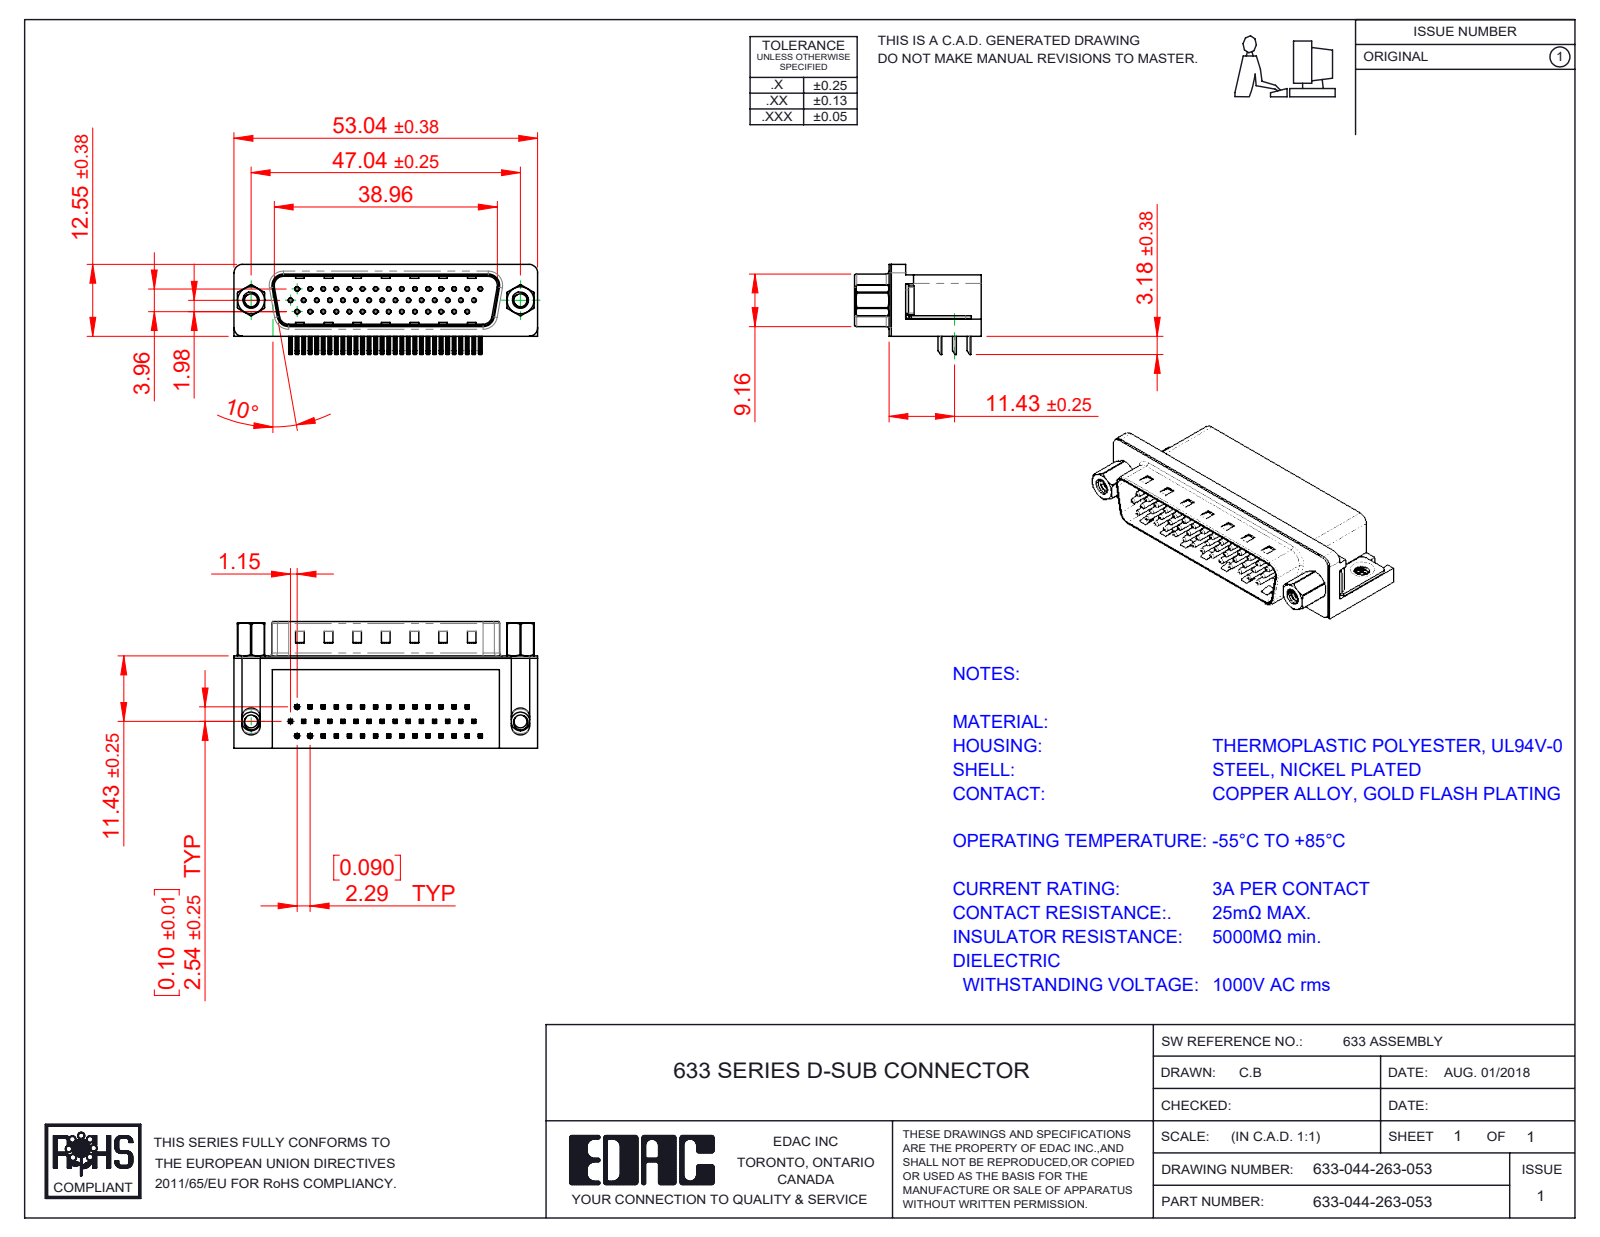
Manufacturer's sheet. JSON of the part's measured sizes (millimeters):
{"part_name": "633 Housing_44 Contact; 633 Contact Middle; 633 Contact Top; 633 4-40 Threaded Rivet (+5 more)", "step_written_by": "SolidWorks 2016 (CONFIG_CONTROL_DESIGN)", "units": "millimeters", "bodies": {"solids": 52, "faces": 3840, "planar": 2339, "cylindrical": 1136, "other": 365}, "overall_size": [53.04, 22.1, 15.73], "volume_mm3": 8329, "surface_area_mm2": 10751, "round_holes": [[0.35, 44], [0.8, 44], [2.26, 4], [2.29, 2], [4, 2], [4.8, 2], [5, 2]], "round_bosses_or_shafts": [[0.75, 44], [4.9, 2], [4.75, 2], [3.9, 2], [3.26, 2], [2.79, 2]], "partial_cylinders_radius": [[0.25, 184], [0.12, 88], [1, 16], [0.5, 9], [1.6, 8], [1.5, 7], [0.9, 4], [2, 4]], "face_to_face_distances": [0.4, 10.35, 15.7, 8.76, 2.9, 2.5, 16.1, 2.1, 10.7, 2.54], "hole_center_spacings": [2.29, 4.57, 4.58, 2.28, 6.87, 9.16, 11.45, 2.27]}
